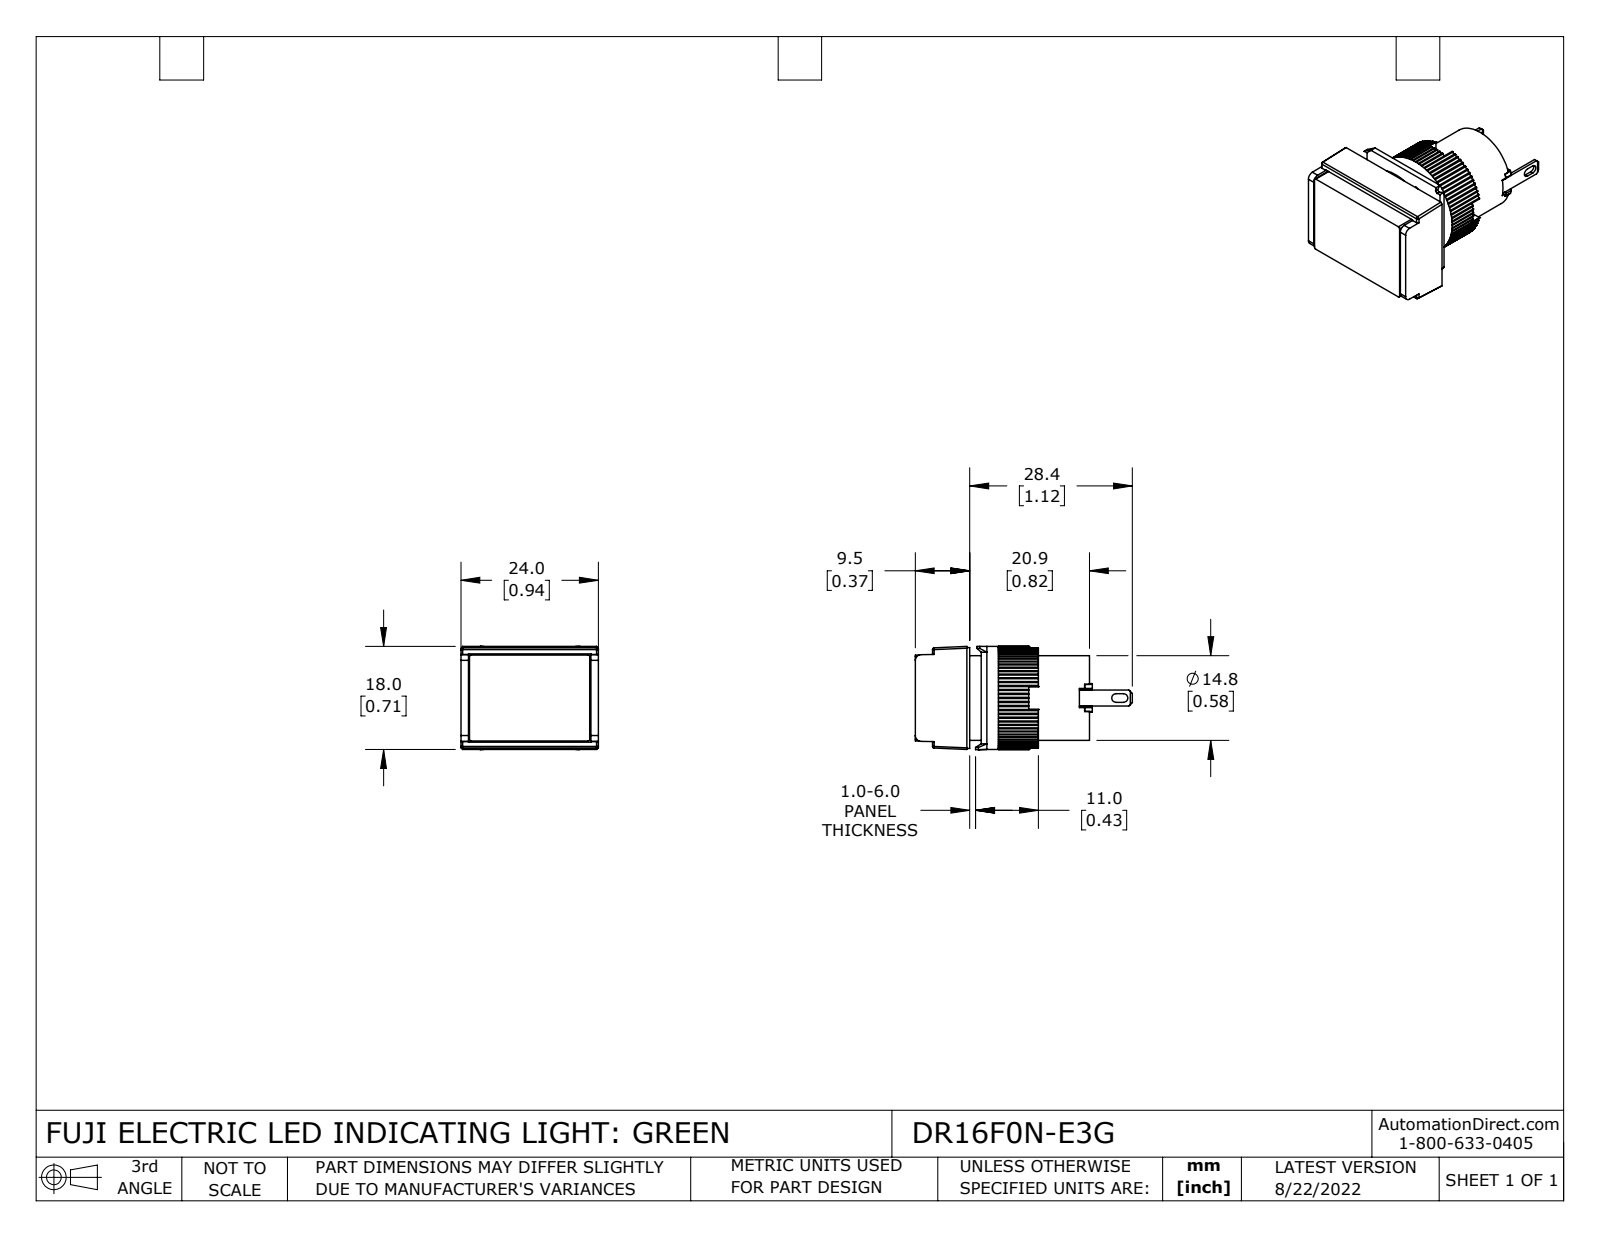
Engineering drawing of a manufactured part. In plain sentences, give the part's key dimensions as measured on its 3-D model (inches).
The part is named "DR16F0N-E3G". Its 3-D file was written by "SolidWorks 2021 (CONFIG_CONTROL_DESIGN)". It is 10 solids with 501 faces: 322 planar, 175 cylindrical and 4 other. Overall it measures 1.492 by 0.945 by 0.709 inches. Its volume is 0.448 cubic inches and its surface area 8.955 square inches. Round holes: 1 of diameter 0.543, 1 of diameter 0.583. Round bosses or shafts: 1 of diameter 0.709, 1 of diameter 0.693. Partial cylindrical surfaces (rounded edges, fillets, slot ends): 80 of radius 0.01, 8 of radius 0.008, 6 of radius 0.012, 2 of radius 0.03, 2 of radius 0.039. The main face-to-face distances are 0.213, 0.354, 0.142, 0.35, 0.492, 0.138, 0.843, 0.705, 0.453, 0.059.
